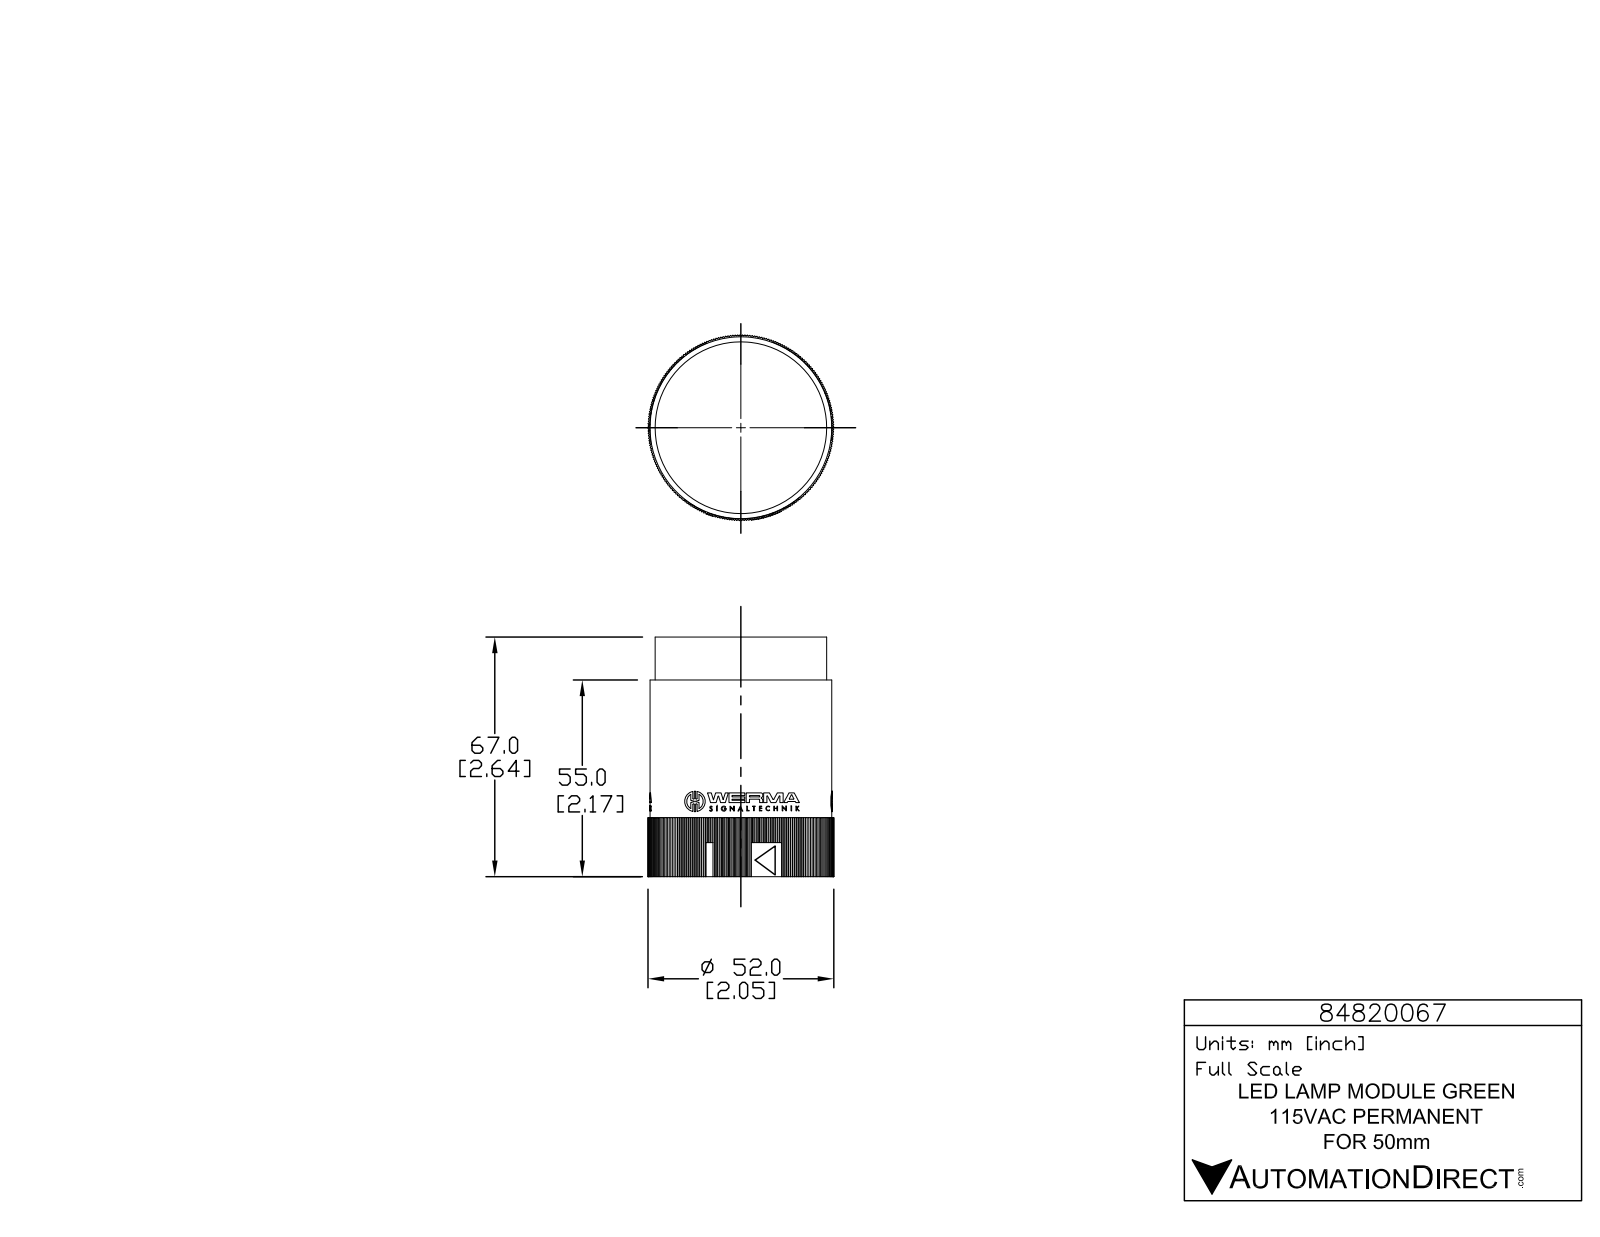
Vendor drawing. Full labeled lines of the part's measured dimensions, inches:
Part name (STEP PRODUCT): 84820067
STEP written by: SolidWorks 2015 (AUTOMOTIVE_DESIGN)
Units: inches
Bodies: 1 solid, 1265 faces (1020 planar, 245 cylindrical, 0 other)
Overall size (bounding box): 2.638 × 2.047 × 2.047
Volume: 6.873 in³ · Surface area: 27.62 in²
Round holes (diameter × count): ⌀0.039 ×3, ⌀1.898 ×1
Round bosses / shafts (diameter × count): ⌀0.226 ×3, ⌀0.056 ×3, ⌀2.002 ×1, ⌀1.89 ×1
Partial cylindrical surfaces — rounded edges, fillets, slot ends (radius × count): R0.008 ×6, R0.008 ×6, R0.008 ×6, R0.131 ×6, R0.004 ×3, R0.005 ×3, R0.008 ×3, R0.008 ×3
Main face-to-face distances: 2.165, 1.428, 1.429, 1.429, 0.472, 2.638, 1.428, 1.428, 1.693, 1.988
